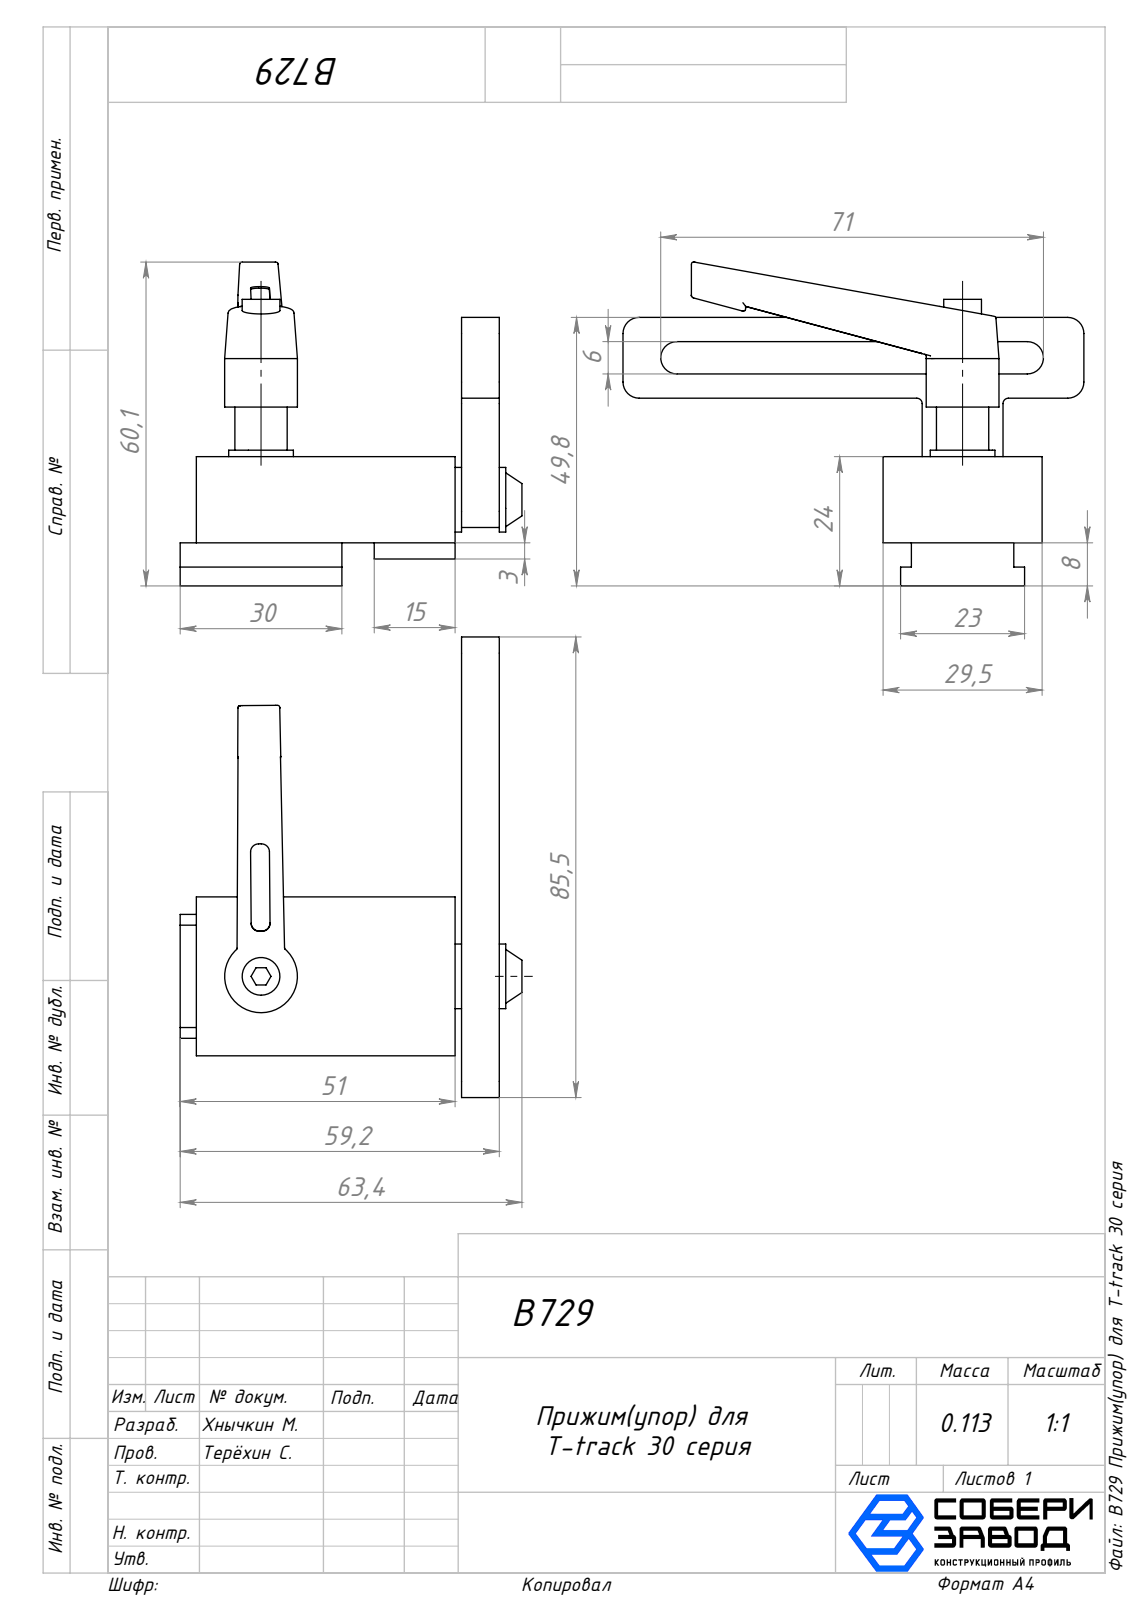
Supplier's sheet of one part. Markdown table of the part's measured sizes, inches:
| quantity | value |
| --- | --- |
| part name | B729 Шайба_00; В729 Винт М6_00; B729 Ручка_00; A395 Винт с рукояткой М6х25_Резьба схематическая (+3 more) |
| STEP written by | SolidWorks 2025 (AUTOMOTIVE_DESIGN) |
| units | inches |
| bodies | 8 solids, 175 faces (78 planar, 44 cylindrical, 53 other) |
| overall size | 3.366 × 2.496 × 2.367 |
| volume | 2.539 in³ |
| surface area | 28.39 in² |
| round holes (diameter × count) | 0.197 × 2, 0.244 × 2, 0.236 × 1, 0.248 × 1 |
| round bosses / shafts (diameter × count) | 0.472 × 2, 0.531 × 1, 0.382 × 1, 0.276 × 1, 0.236 × 1 |
| partial cylindrical surfaces (radius × count) | 0.118 × 8, 0.059 × 4, 0.039 × 2 |
| main face-to-face distances | 0.276, 0.63, 0.177, 0.413, 0.047, 1.161, 0.315, 0.945, 0.323, 1.648 |
